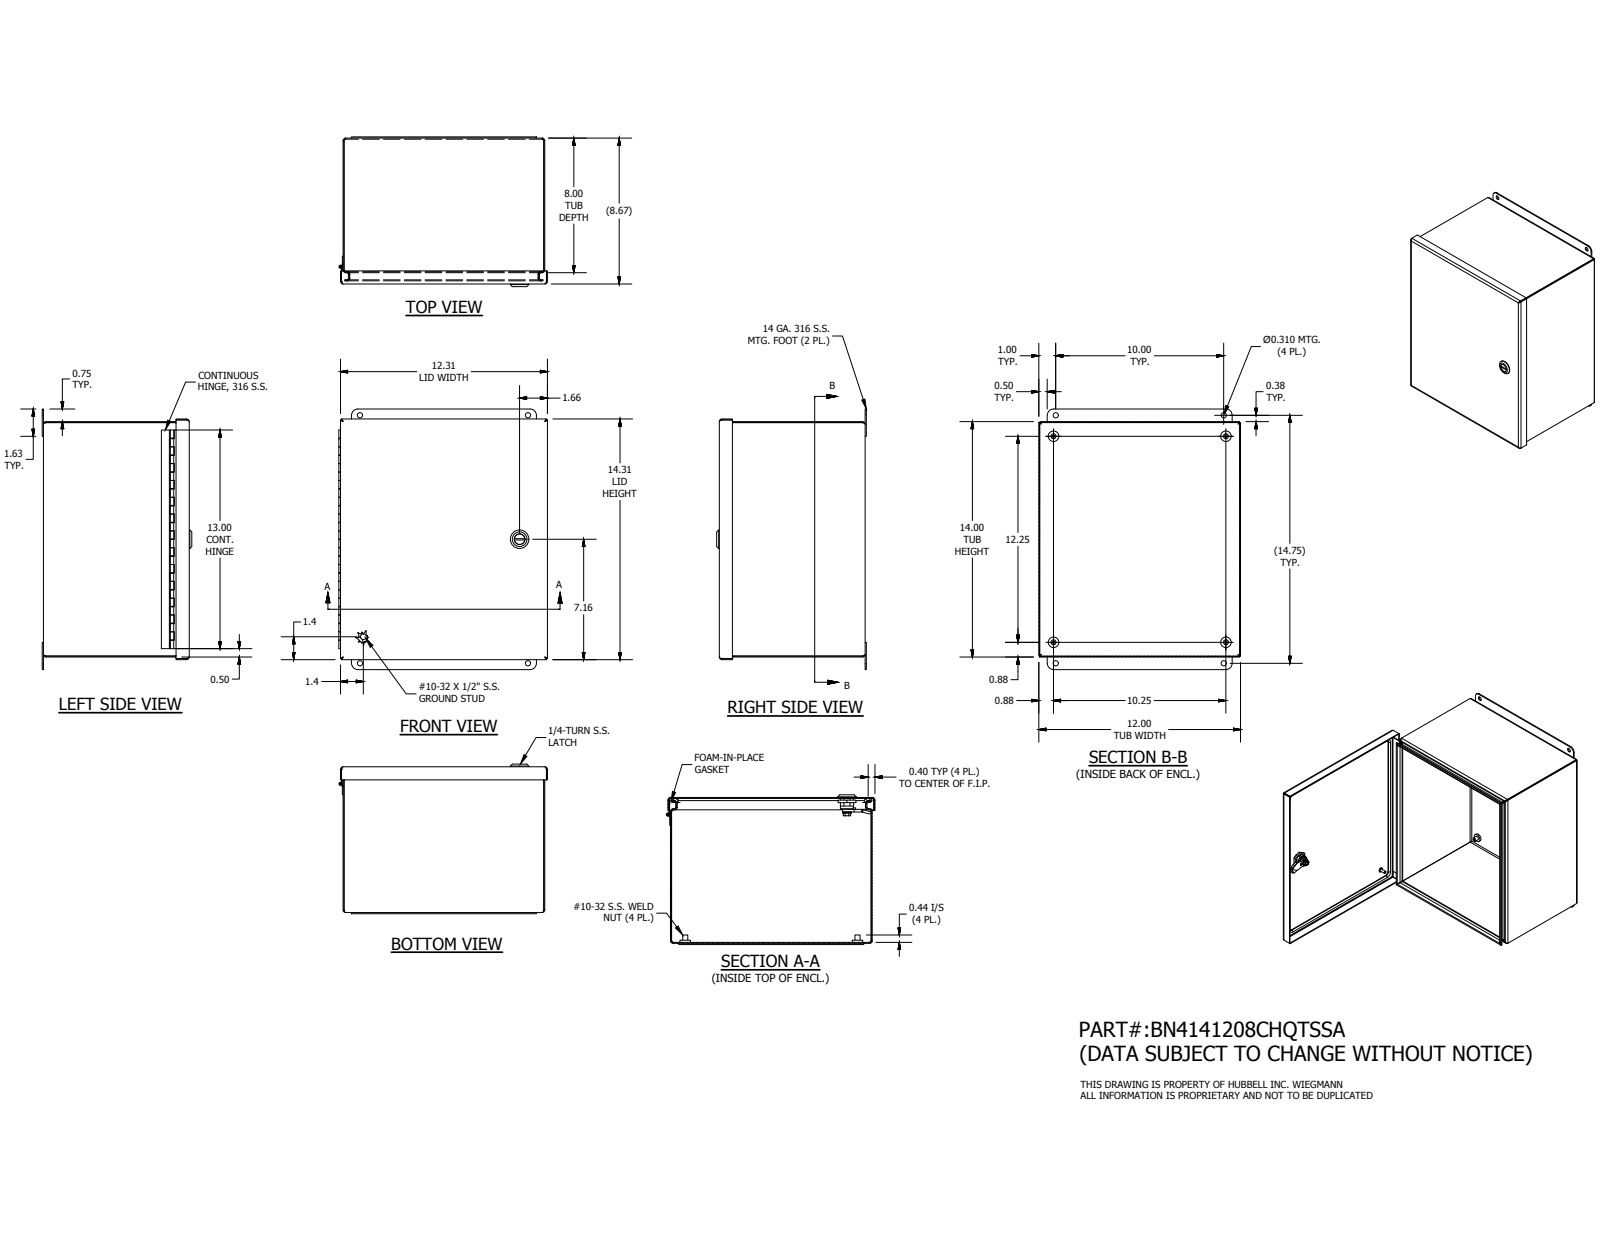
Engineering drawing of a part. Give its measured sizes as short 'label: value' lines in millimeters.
name: BN41412CHQTSSALID; 14x12; 348131; 32885LH (+8 more)
written by: Autodesk Inventor 2016 (AUTOMOTIVE_DESIGN)
unit: mm
bodies: 21 solids, 691 faces (378 planar, 216 cylindrical, 97 other)
size: 393.7 × 315.26 × 226.19
volume: 952 305 mm³; area: 1 208 000 mm²
holes: 4× ⌀3.96, 4× ⌀7.87, 1× ⌀2.96, 1× ⌀5, 1× ⌀8, 1× ⌀10, 1× ⌀10.2, 1× ⌀16.1, 1× ⌀20.38
bosses: 4× ⌀15.88, 4× ⌀7.62, 1× ⌀28, 1× ⌀19.8, 1× ⌀16, 1× ⌀15.2, 1× ⌀13.5, 1× ⌀12.8
rounds: 20× R2.38, 20× R3.88, 16× R3.17, 8× R0.5, 4× R4, 4× R9.53, 2× R2.31, 1× R6.45
face distances: 1.5, 1.49, 354.1, 218.79, 220.28, 217.29, 218.78, 304.8, 303.3, 303.31
hole spacings: 31.91, 342.91, 254, 259.12, 259.13, 260.35, 305.47, 311.15
